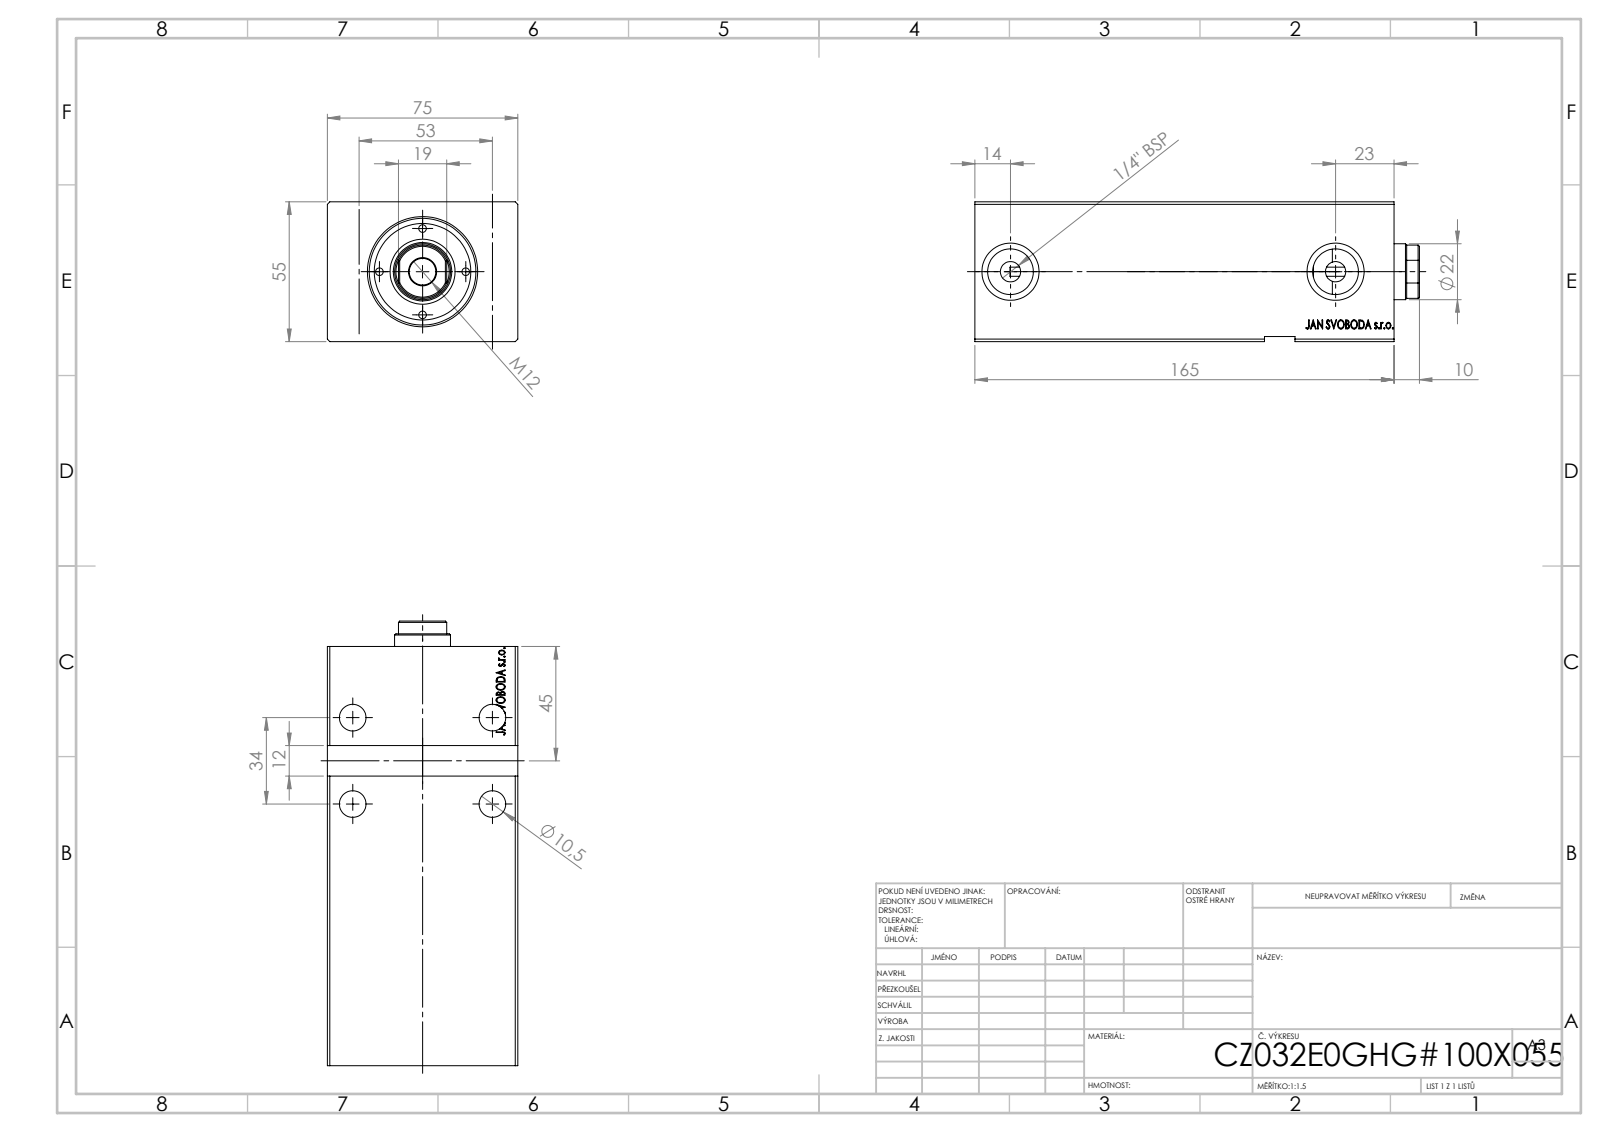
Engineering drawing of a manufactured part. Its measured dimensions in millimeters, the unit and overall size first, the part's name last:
Units: millimetres
Overall size (bounding box): 165 × 75 × 55
Round holes (diameter × count): ⌀8 ×4, ⌀10.5 ×4, ⌀18 ×2, ⌀22.5 ×2, ⌀32 ×1, ⌀36 ×1, ⌀42 ×1
Main face-to-face distances: 55, 75, 165, 13.6, 164.8, 2, 53, 151.2, 13.8, 10
Hole centre spacings: 34, 55, 64.66, 18.2, 33.87, 37.83, 47.41, 80.92
Volume: 525 012 mm³ · Surface area: 74 472 mm²
Bodies: 1 solid, 764 faces (377 planar, 31 cylindrical, 356 other)
STEP written by: SolidWorks 2019 (CONFIG_CONTROL_DESIGN)
